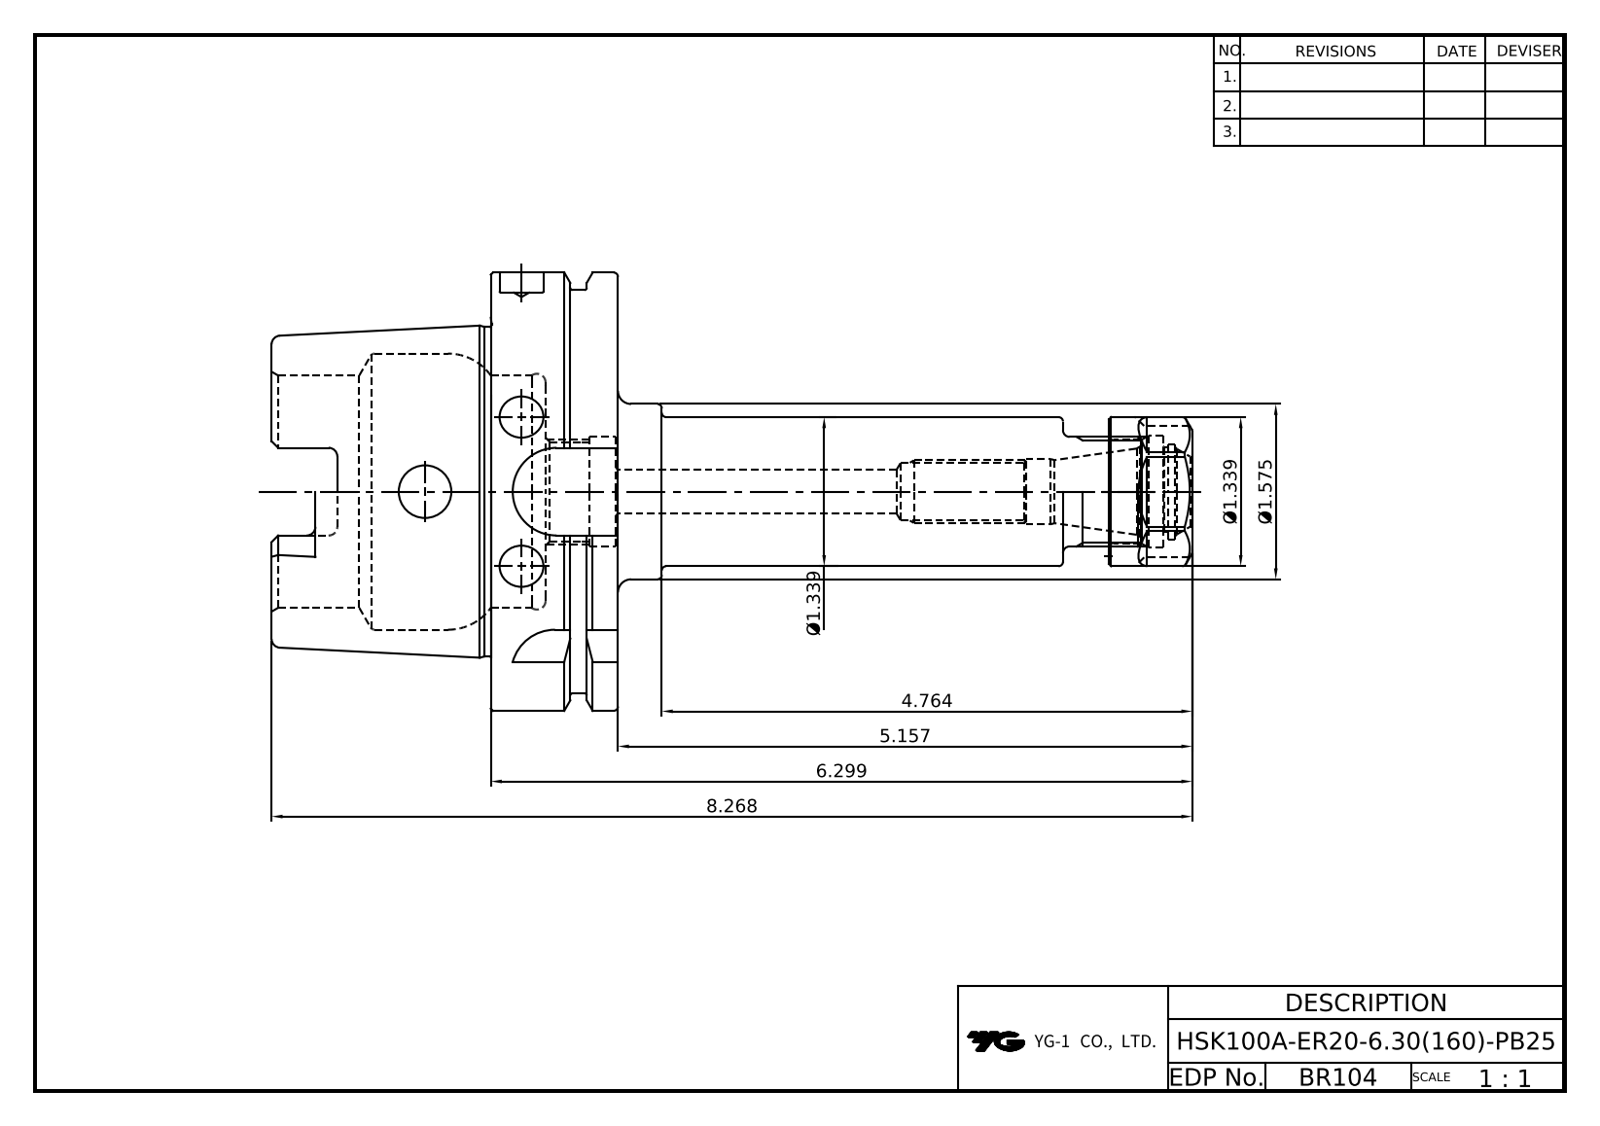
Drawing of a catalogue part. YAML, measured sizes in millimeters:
part_name: "LO-HSK100A-ER20-6.30; ER20NUT"
step_written_by: "Autodesk Inventor 2025 (AUTOMOTIVE_DESIGN)"
units: millimeters
bodies: {solids: 2, faces: 153, planar: 58, cylindrical: 43, other: 52}
overall_size: [210, 100, 100]
volume: 352846
surface_area: 71418
round_holes:
  - {diameter: 10, count: 2}
  - {diameter: 12, count: 1}
  - {diameter: 12.57, count: 1}
  - {diameter: 14.9, count: 1}
  - {diameter: 16, count: 1}
  - {diameter: 18.4, count: 1}
  - {diameter: 21.76, count: 1}
  - {diameter: 22.38, count: 1}
  - {diameter: 23.5, count: 1}
  - {diameter: 25.5, count: 1}
  - {diameter: 53, count: 1}
  - {diameter: 63, count: 1}
round_bosses_or_shafts:
  - {diameter: 100, count: 1}
  - {diameter: 92, count: 1}
  - {diameter: 75.41, count: 1}
  - {diameter: 40, count: 1}
  - {diameter: 34, count: 1}
  - {diameter: 25, count: 1}
partial_cylinders:
  - {radius: 2, count: 6}
  - {radius: 4.88, count: 4}
  - {radius: 10, count: 4}
face_to_face_distances: [29, 16.5, 12.5, 79, 62.5, 50, 10, 30, 88, 210]
